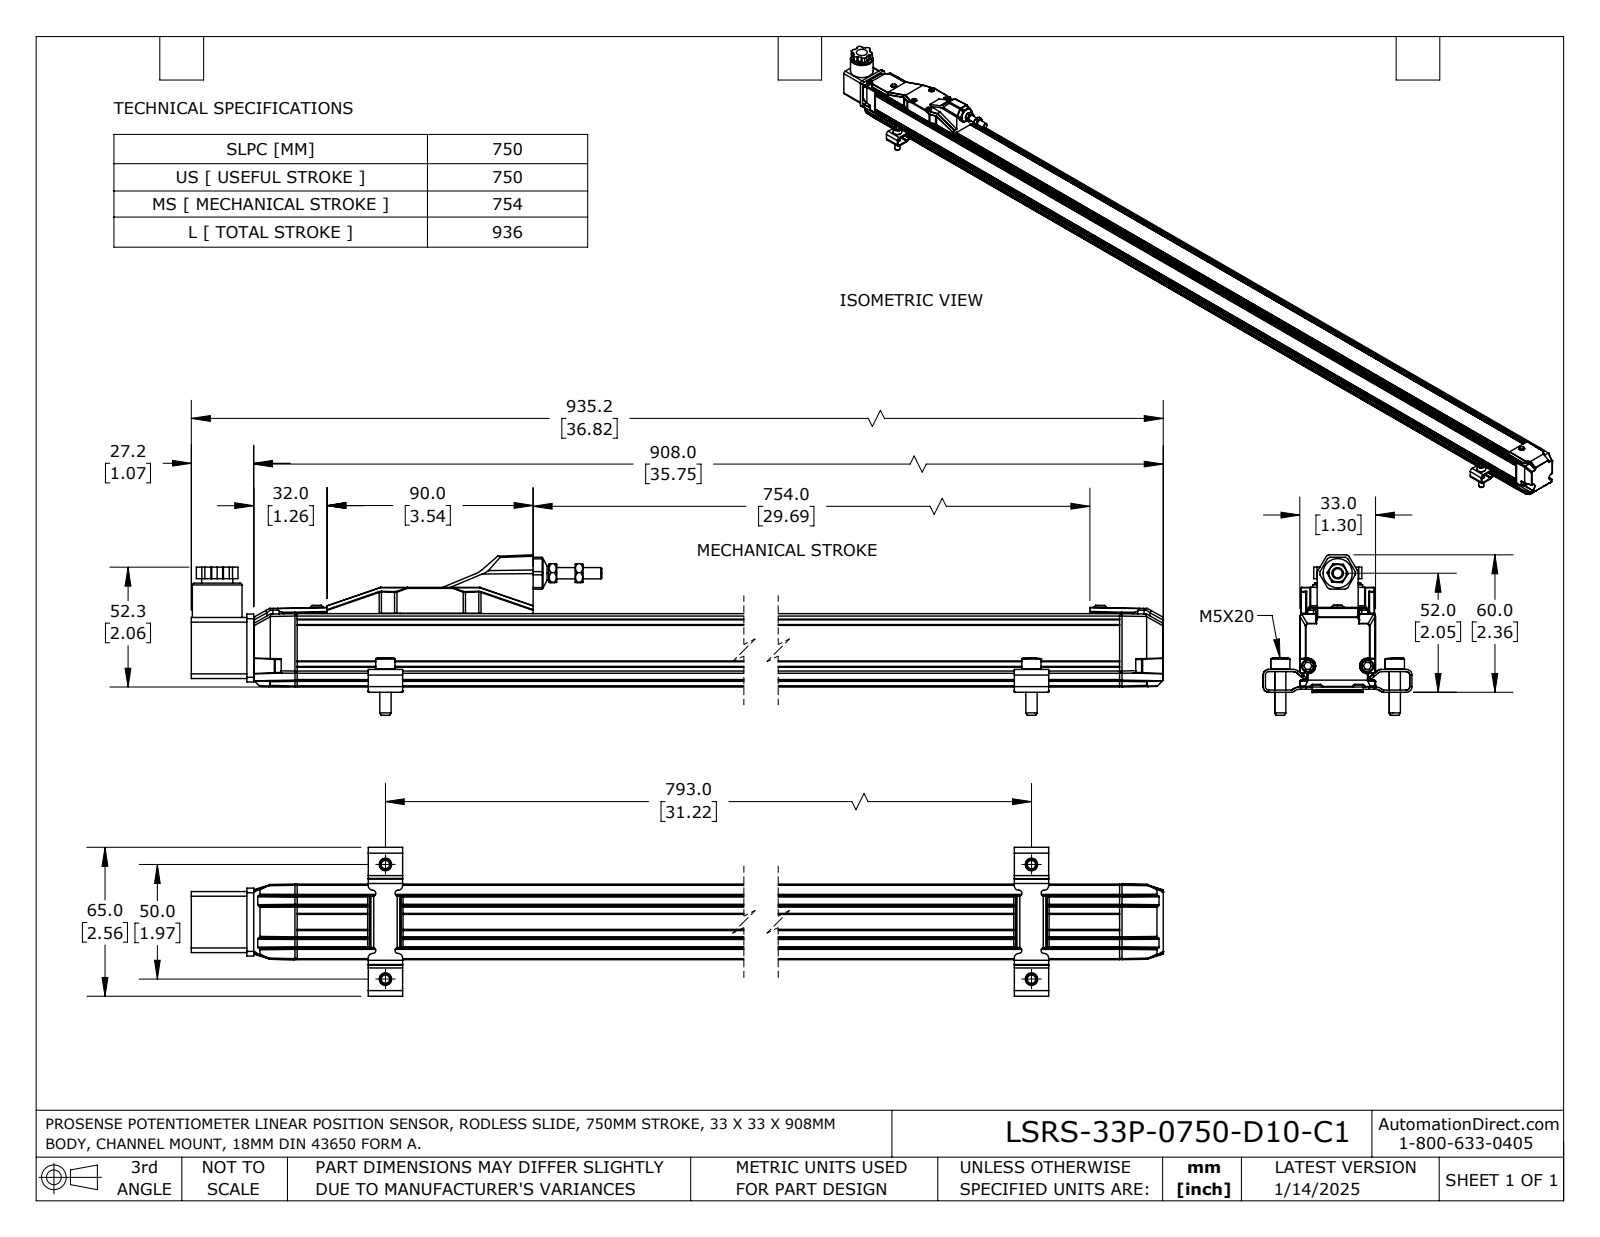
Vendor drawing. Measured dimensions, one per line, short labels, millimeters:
name: LSRS-33P-0750-D10-C1
written by: SolidWorks 2023 (AUTOMOTIVE_DESIGN)
unit: mm
bodies: 11 solids, 1314 faces (823 planar, 359 cylindrical, 132 other)
size: 935.2 × 70 × 65
volume: 886 700 mm³; area: 207 300 mm²
holes: 4× ⌀4.7, 4× ⌀5.5, 2× ⌀2.7, 2× ⌀3.3, 1× ⌀4, 1× ⌀5, 1× ⌀5.3, 1× ⌀5.9, 1× ⌀6, 1× ⌀7, 1× ⌀10, 1× ⌀10.5
bosses: 4× ⌀8.4, 4× ⌀4.9, 4× ⌀4.6, 4× ⌀2.9, 2× ⌀5.6, 2× ⌀5.5, 2× ⌀3, 2× ⌀2.5
rounds: 78× R0.5, 62× R0.2, 44× R2, 26× R3, 10× R1, 8× R1.3, 8× R1.5, 8× R4
face distances: 33, 3, 31.6, 29.6, 6, 25.6, 0.9, 0.4, 32.6, 11.3
hole spacings: 15.2, 20, 23.7, 31, 32.7, 42.5, 50, 763.6
